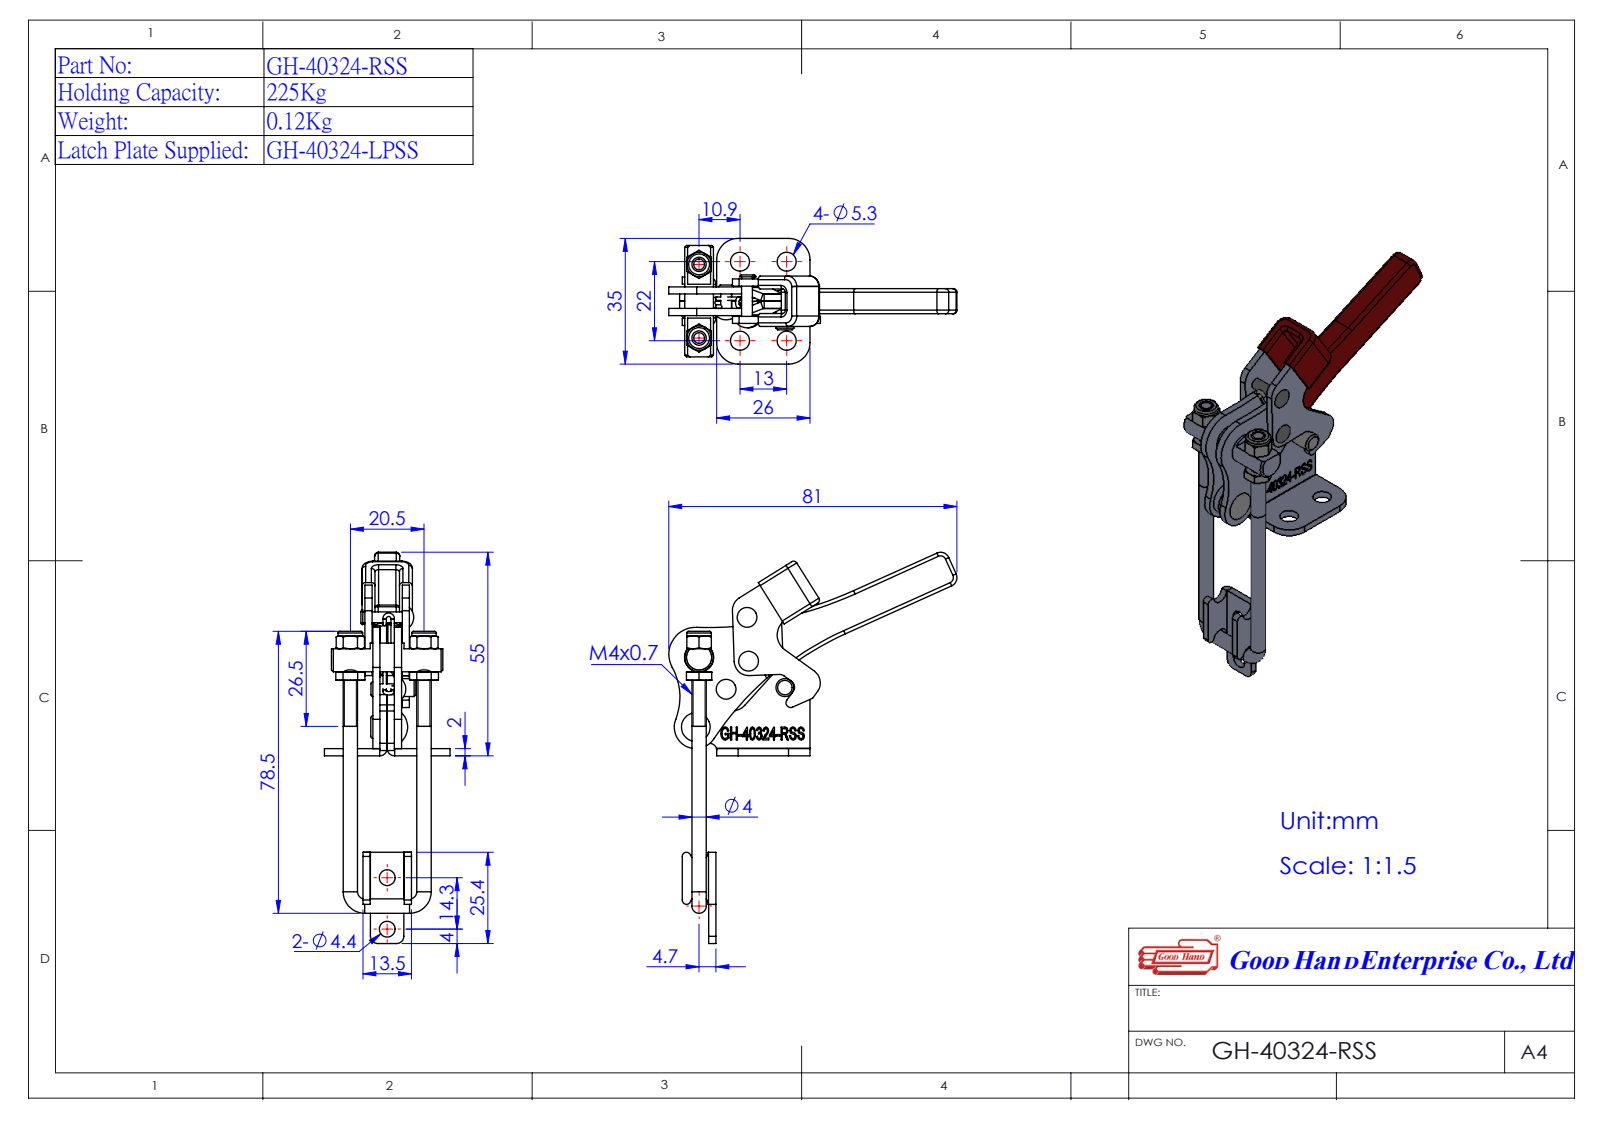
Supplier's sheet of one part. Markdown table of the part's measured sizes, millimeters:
| quantity | value |
| --- | --- |
| part name | Group3^GH-40324-R(簡化); 14032414-2^GH-40324-R(簡化); Group2^GH-40324-R(簡化); Group1^GH-40324-R(簡化) (+2 more) |
| STEP written by | SolidWorks 2016 (AUTOMOTIVE_DESIGN) |
| units | millimeters |
| bodies | 7 solids, 827 faces (374 planar, 180 cylindrical, 273 other) |
| overall size | 108.87 × 80.22 × 34 |
| volume | 17 656 mm³ |
| surface area | 15 877 mm² |
| round holes (diameter × count) | 5.3 × 4, 4 × 3, 3.3 × 2, 4.1 × 2, 4.4 × 2, 1.53 × 1, 8 × 1 |
| round bosses / shafts (diameter × count) | 6.8 × 2, 4 × 2, 5 × 1, 3 × 1, 1.47 × 1 |
| partial cylindrical surfaces (radius × count) | 1 × 20, 6 × 5, 0.1 × 4, 0.74 × 4, 2.1 × 4, 2.5 × 4, 2.74 × 4, 0.58 × 3 |
| main face-to-face distances | 2, 8.2, 2.2, 6, 4, 1.5, 5.5, 0.5, 7.5, 0.7 |
| hole center spacings | 11.41, 13, 22, 24.11, 24.4, 25.55, 32.35, 11.24 |
